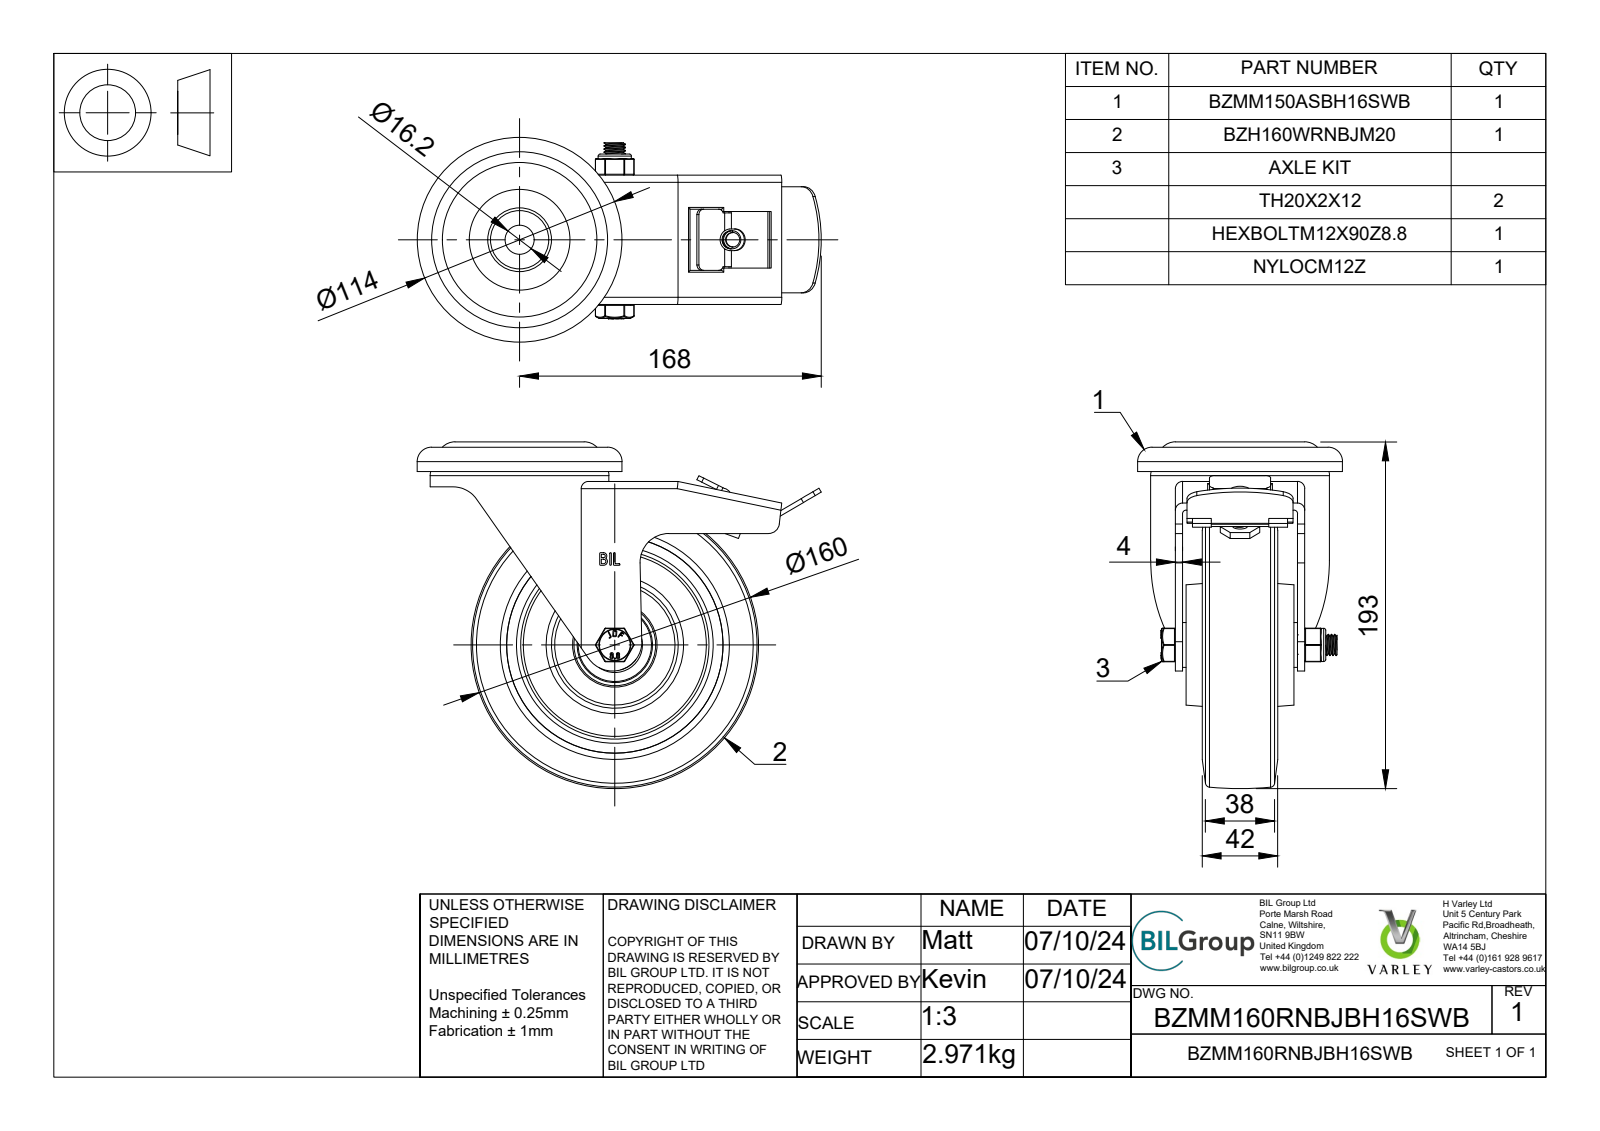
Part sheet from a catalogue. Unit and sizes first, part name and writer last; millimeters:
Units: millimetres
Overall size (bounding box): 225 × 193 × 114
Round holes (diameter × count): ⌀10 ×1, ⌀10.27 ×1, ⌀12 ×1, ⌀12.2 ×1, ⌀14 ×1, ⌀16.2 ×1, ⌀20 ×1, ⌀28.5 ×1, ⌀30.8 ×1, ⌀40.3 ×1, ⌀40.5 ×1, ⌀41 ×1
Round bosses / shafts (diameter × count): ⌀114 ×1, ⌀99.5 ×1, ⌀74 ×1, ⌀47 ×1, ⌀40.8 ×1, ⌀32.5 ×1, ⌀31.3 ×1, ⌀27 ×1
Partial cylindrical surfaces — rounded edges, fillets, slot ends (radius × count): R0.5 ×24, R2 ×8, R1 ×6, R0.47 ×4, R0.9 ×4, R3 ×4, R4 ×4, R6 ×3
Main face-to-face distances: 4, 17, 25, 28, 36, 11, 53, 1, 8, 26
Volume: 904 283 mm³ · Surface area: 291 323 mm²
Bodies: 40 solids, 1257 faces (558 planar, 252 cylindrical, 447 other)
Part name (STEP PRODUCT): BZMM160RNBJBH16SWB v2; BZMM150ASBH16SWB - 64 v1; ZINC PLATED, PRESSED STEEL HEAD; ZINC PLATED, PRESSED STEEL FORKS (+8 more)
STEP written by: Autodesk Translation Framework v13.20.0.188 (AUTOMOTIVE_DESIGN)
